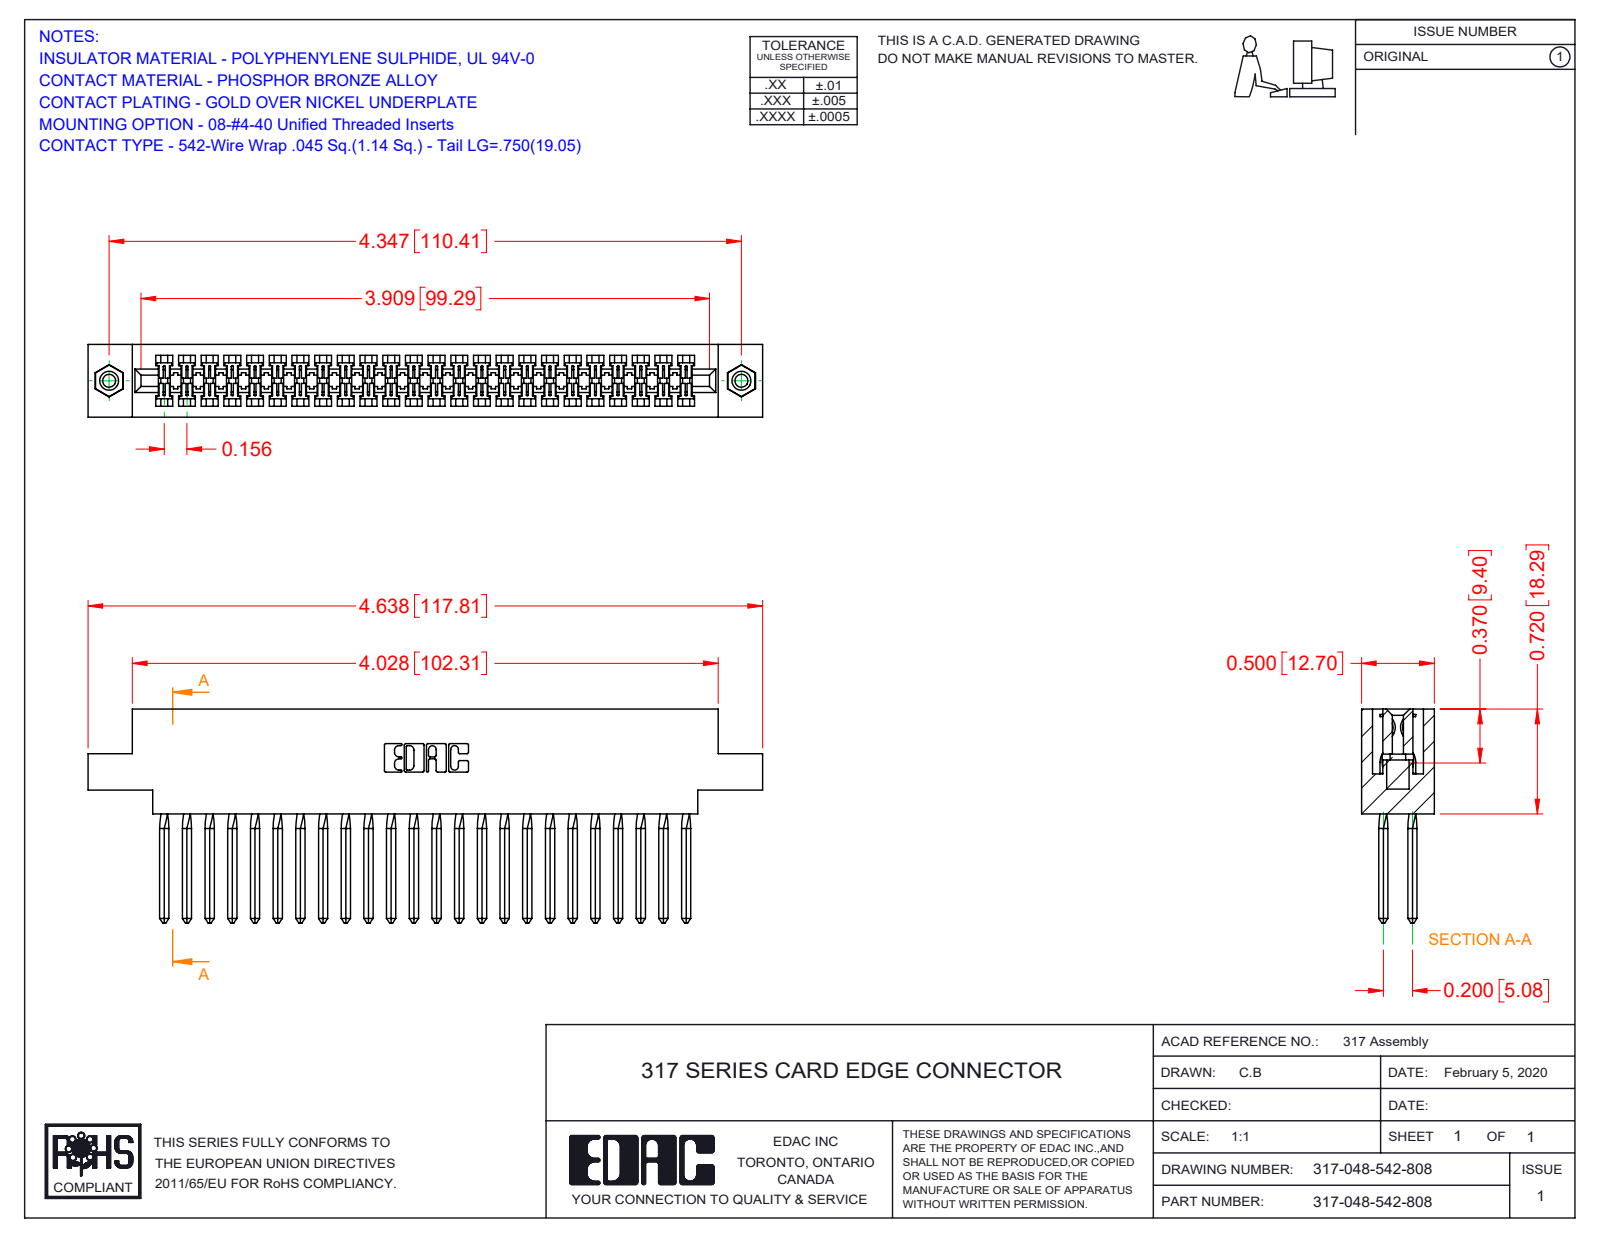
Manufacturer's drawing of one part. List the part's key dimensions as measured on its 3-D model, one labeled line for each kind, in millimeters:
Part name (STEP PRODUCT): 345-250-001_345-250-003-102; 317-290-003_542; 317 Part_.156 Dia - TI; 317-048-542-878
STEP written by: SolidWorks 2016 (CONFIG_CONTROL_DESIGN)
Units: millimetres
Bodies: 51 solids, 2898 faces (2298 planar, 392 cylindrical, 208 other)
Overall size (bounding box): 117.8 × 37.3 × 12.7
Volume: 18 710 mm³ · Surface area: 25 470 mm²
Round holes (diameter × count): ⌀2.3 ×2, ⌀3.2 ×2, ⌀4 ×2
Round bosses / shafts (diameter × count): ⌀3.9 ×2
Partial cylindrical surfaces — rounded edges, fillets, slot ends (radius × count): R0.2 ×96, R0.3 ×22, R0.2 ×6, R0.8 ×6, R0.7 ×3, R1.9 ×2, R2.3 ×2, R2.5 ×2
Main face-to-face distances: 12.7, 1.9, 10.8, 8.9, 2.8, 5.1, 2.9, 3.5, 1.2, 18.3
Hole centre spacings: 110.4
